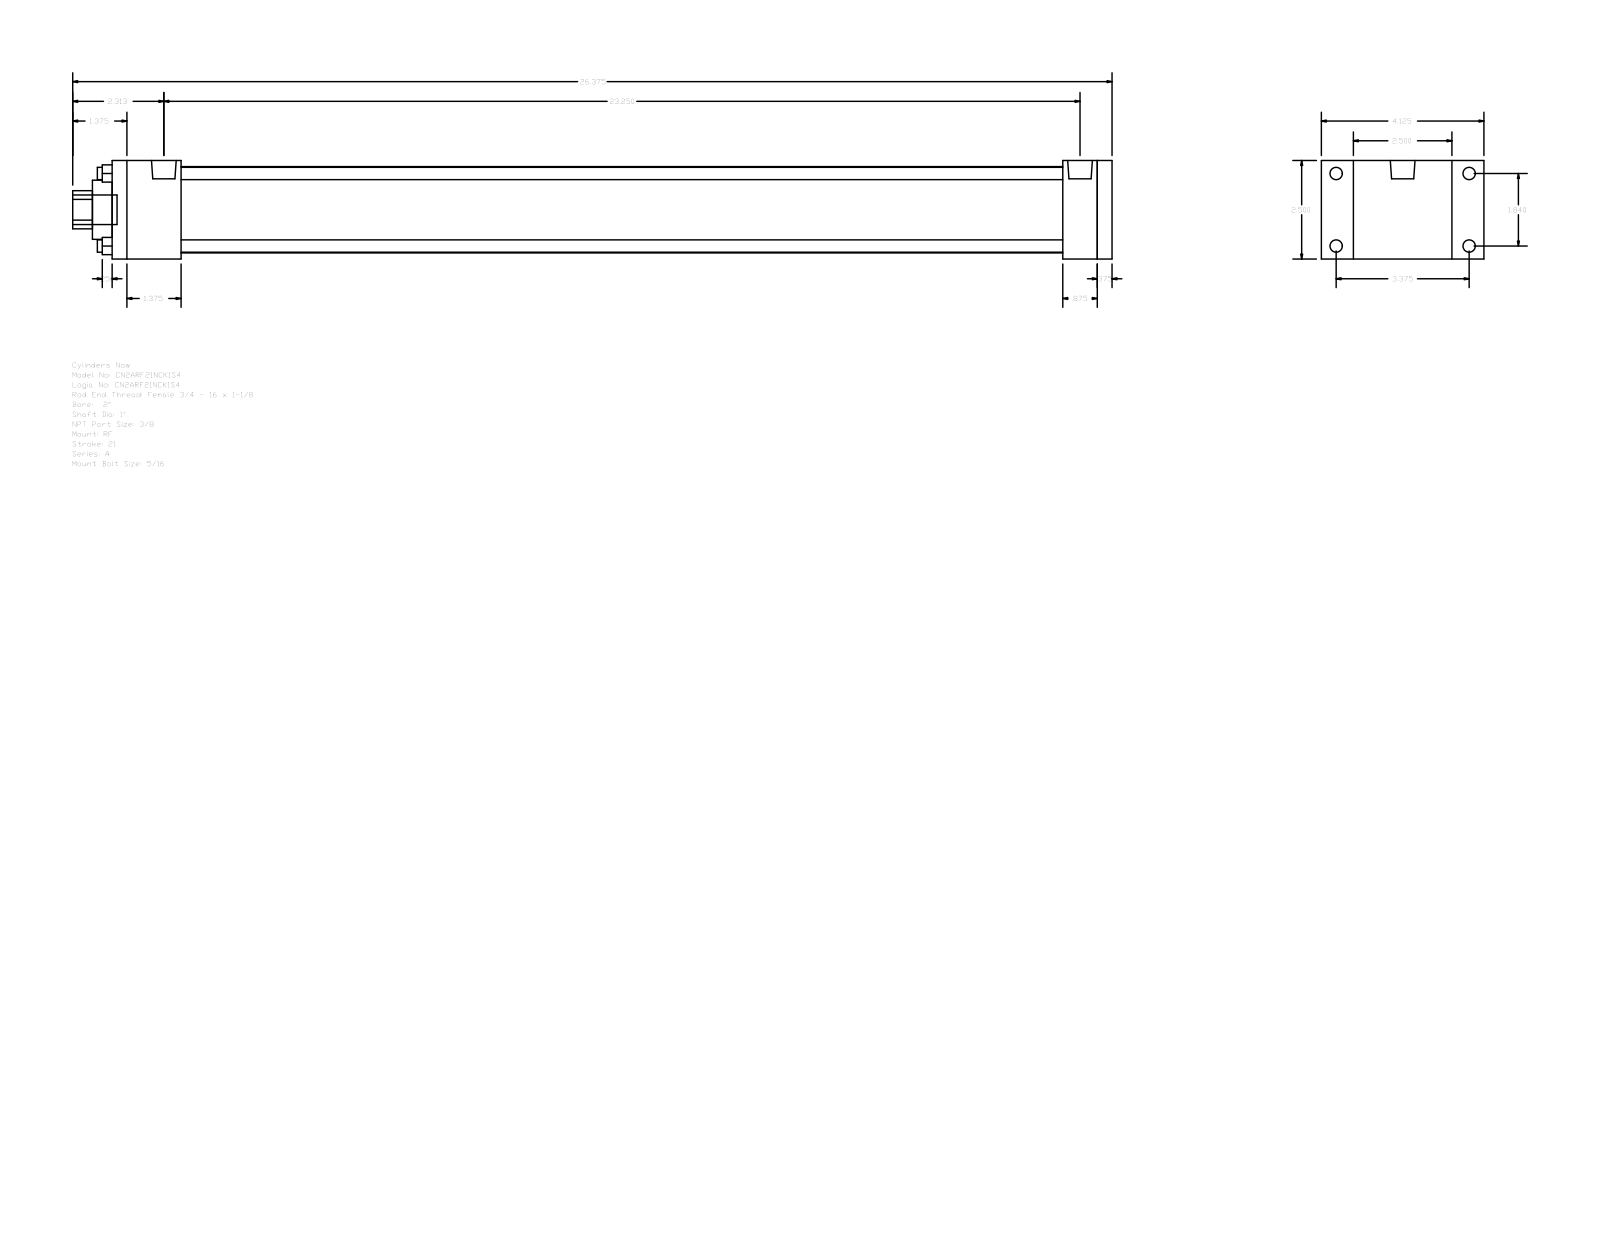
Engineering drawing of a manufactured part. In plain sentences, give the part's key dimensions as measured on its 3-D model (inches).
The part is named "A_RF__0200_1". Its 3-D file was written by "GSSL Pune (CONFIG_CONTROL_DESIGN)". It is 0 solids with 92 faces: 64 planar, 28 cylindrical and 0 other. Overall it measures 26.375 by 4.125 by 2.5 inches. Round holes: 4 of diameter 0.313, 1 of diameter 1, 1 of diameter 1.5, 1 of diameter 2.19. Round bosses or shafts: 4 of diameter 0.313, 4 of diameter 0.219, 2 of diameter 0.627, 1 of diameter 0.75. Partial cylindrical surfaces (rounded edges, fillets, slot ends): 1 of radius 0.484. The main face-to-face distances are 2.5, 0.375, 25.375, 25, 0.813, 1.75, 23.25, 23.625, 24.125, 22.375. The hole center spacings are 1.301, 1.84, 2.602.
